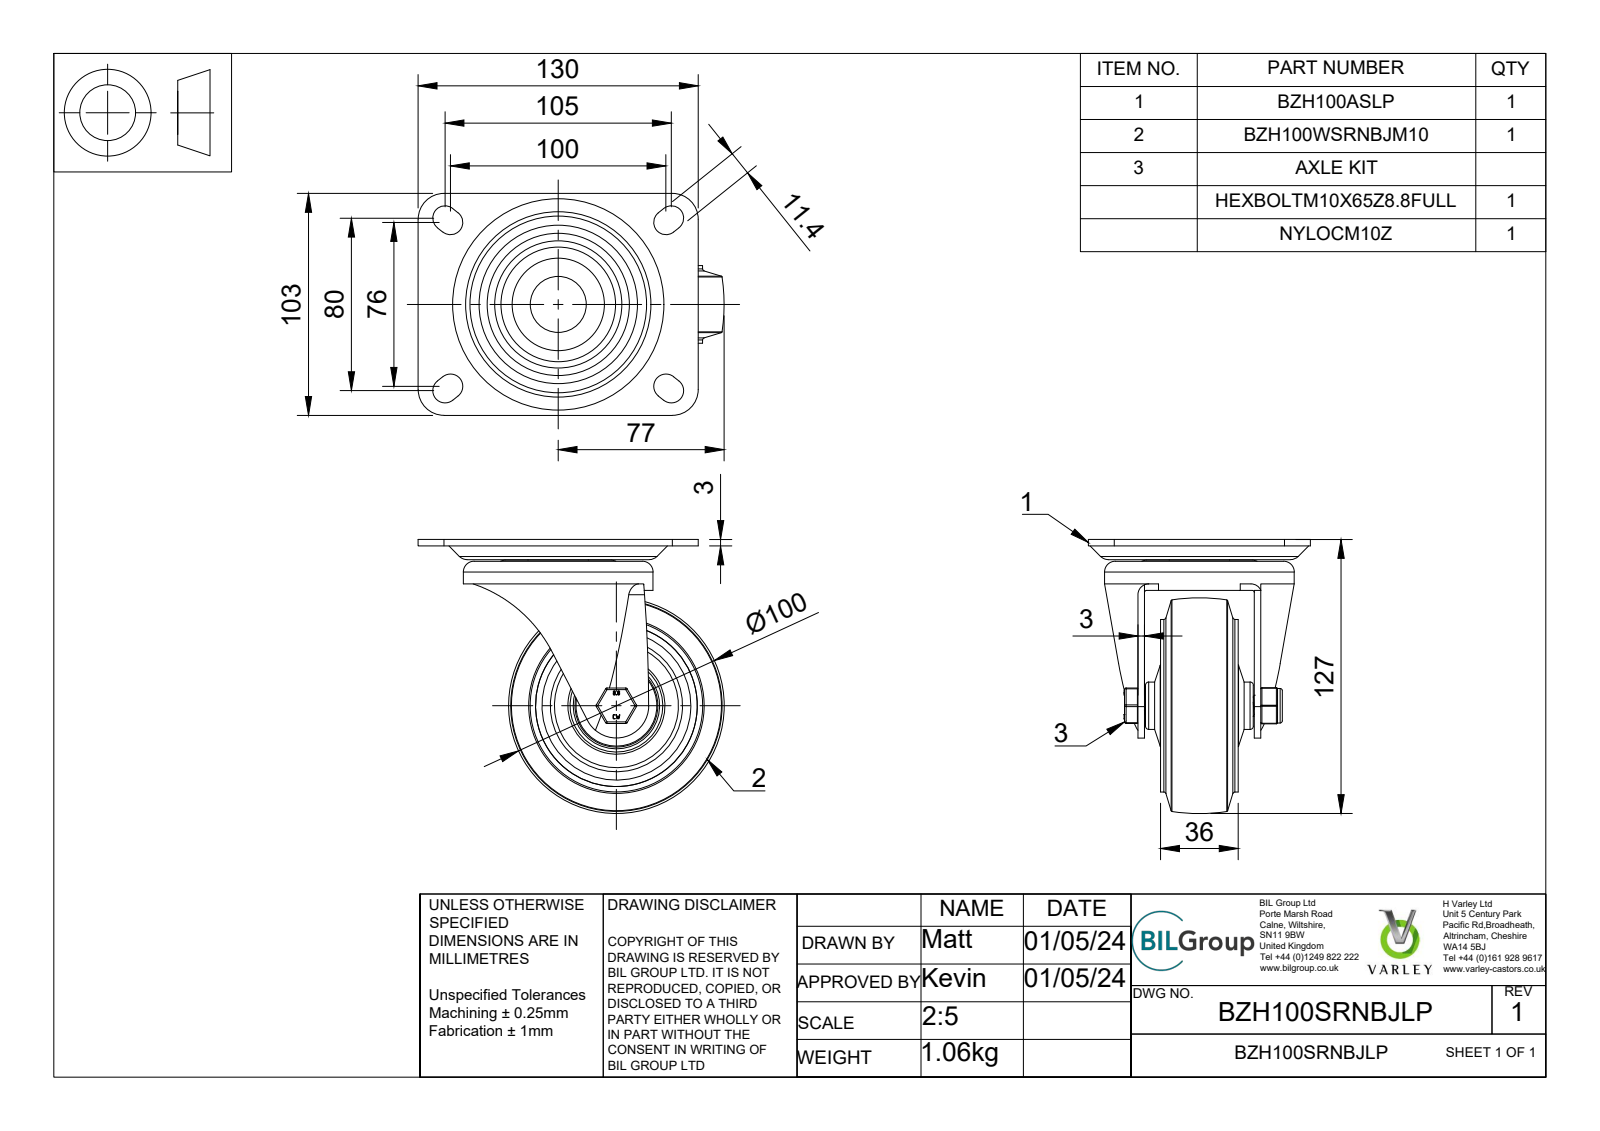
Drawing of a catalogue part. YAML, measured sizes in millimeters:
part_name: "BZH100SRNBJLP v3; BZH100ASLP v1; ZINC PLATED PRESSED STEEL FORK; ZINC PLATED PRESSED STEEL TOP PLATE (+8 more)"
step_written_by: "Autodesk Translation Framework v12.20.1.177 (AUTOMOTIVE_DESIGN)"
units: millimeters
bodies: {solids: 22, faces: 764, planar: 264, cylindrical: 220, other: 280}
overall_size: [142, 127.13, 103]
volume: 284236
surface_area: 141692
round_holes:
  - {diameter: 30, count: 2}
  - {diameter: 10, count: 1}
  - {diameter: 10.2, count: 1}
  - {diameter: 10.5, count: 1}
  - {diameter: 12, count: 1}
  - {diameter: 15, count: 1}
  - {diameter: 20, count: 1}
  - {diameter: 22.5, count: 1}
  - {diameter: 26, count: 1}
  - {diameter: 31, count: 1}
  - {diameter: 32, count: 1}
  - {diameter: 33, count: 1}
round_bosses_or_shafts:
  - {diameter: 28, count: 2}
  - {diameter: 88, count: 1}
  - {diameter: 80, count: 1}
  - {diameter: 43, count: 1}
  - {diameter: 38.5, count: 1}
  - {diameter: 36, count: 1}
  - {diameter: 35, count: 1}
  - {diameter: 30.5, count: 1}
partial_cylinders:
  - {radius: 0.5, count: 18}
  - {radius: 0.75, count: 12}
  - {radius: 5.7, count: 8}
  - {radius: 12, count: 5}
  - {radius: 1, count: 2}
  - {radius: 5, count: 2}
  - {radius: 13.75, count: 1}
  - {radius: 64.34, count: 1}
face_to_face_distances: [3, 10.5, 46.5, 25.5, 22.5, 23, 3.5, 7.5, 15, 21]
